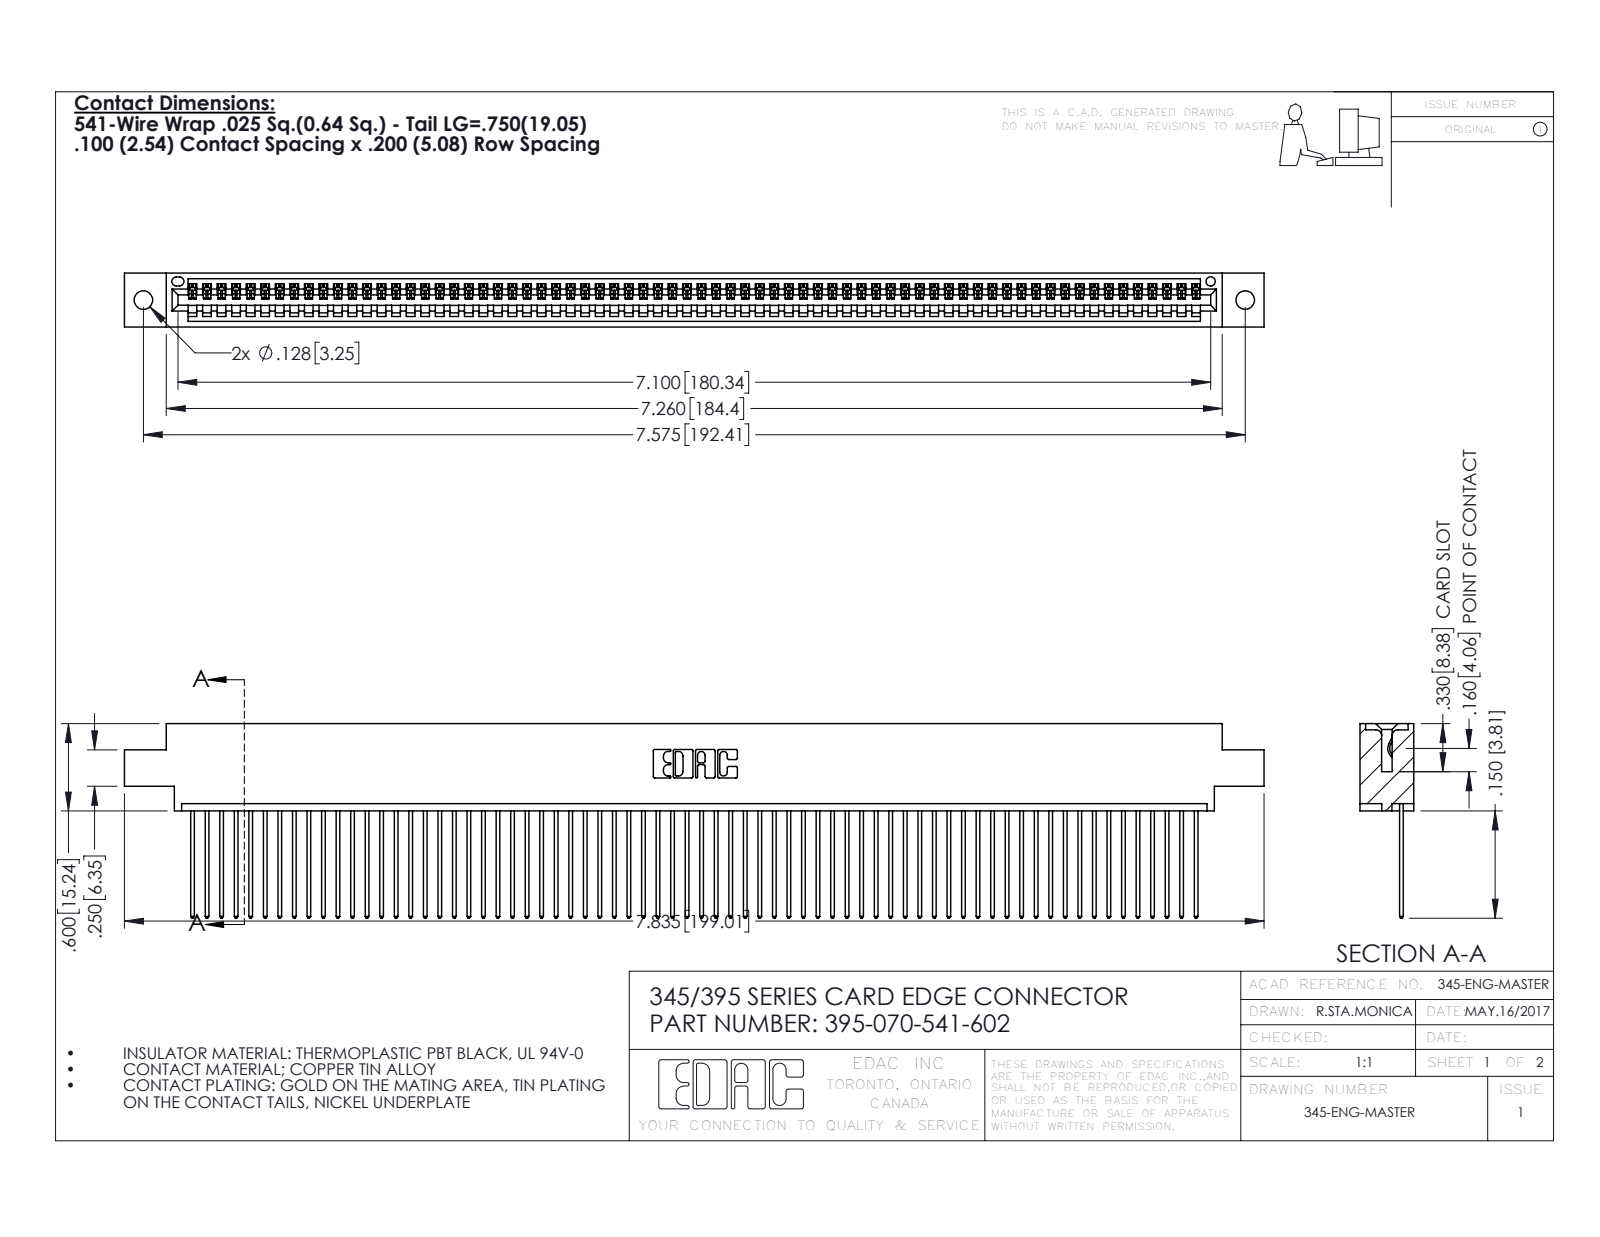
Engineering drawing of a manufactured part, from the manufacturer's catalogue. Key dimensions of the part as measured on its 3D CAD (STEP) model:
Part name (STEP PRODUCT): 345-292-001_345-293-141; 345 Part_0.170 Offset - 0.128 Dia; 395-070-541-602
STEP written by: SolidWorks 2016 (CONFIG_CONTROL_DESIGN)
Units: inches
Bodies: 71 solids, 4190 faces (2884 planar, 1306 cylindrical, 0 other)
Overall size (bounding box): 7.835 × 1.337 × 0.37
Volume: 1.172 in³ · Surface area: 42.05 in²
Round holes (diameter × count): ⌀0.128 ×2, ⌀0.064 ×1
Partial cylindrical surfaces — rounded edges, fillets, slot ends (radius × count): R0.006 ×140, R0.01 ×140, R0.01 ×22, R0.007 ×6, R0.031 ×6, R0.026 ×3, R0.031 ×2, R0.04 ×2
Main face-to-face distances: 0.072, 0.298, 0.098, 0.272, 0.025, 0.37, 0.2, 0.225, 0.175, 0.149
Hole centre spacings: 0.27, 7.339, 7.575
